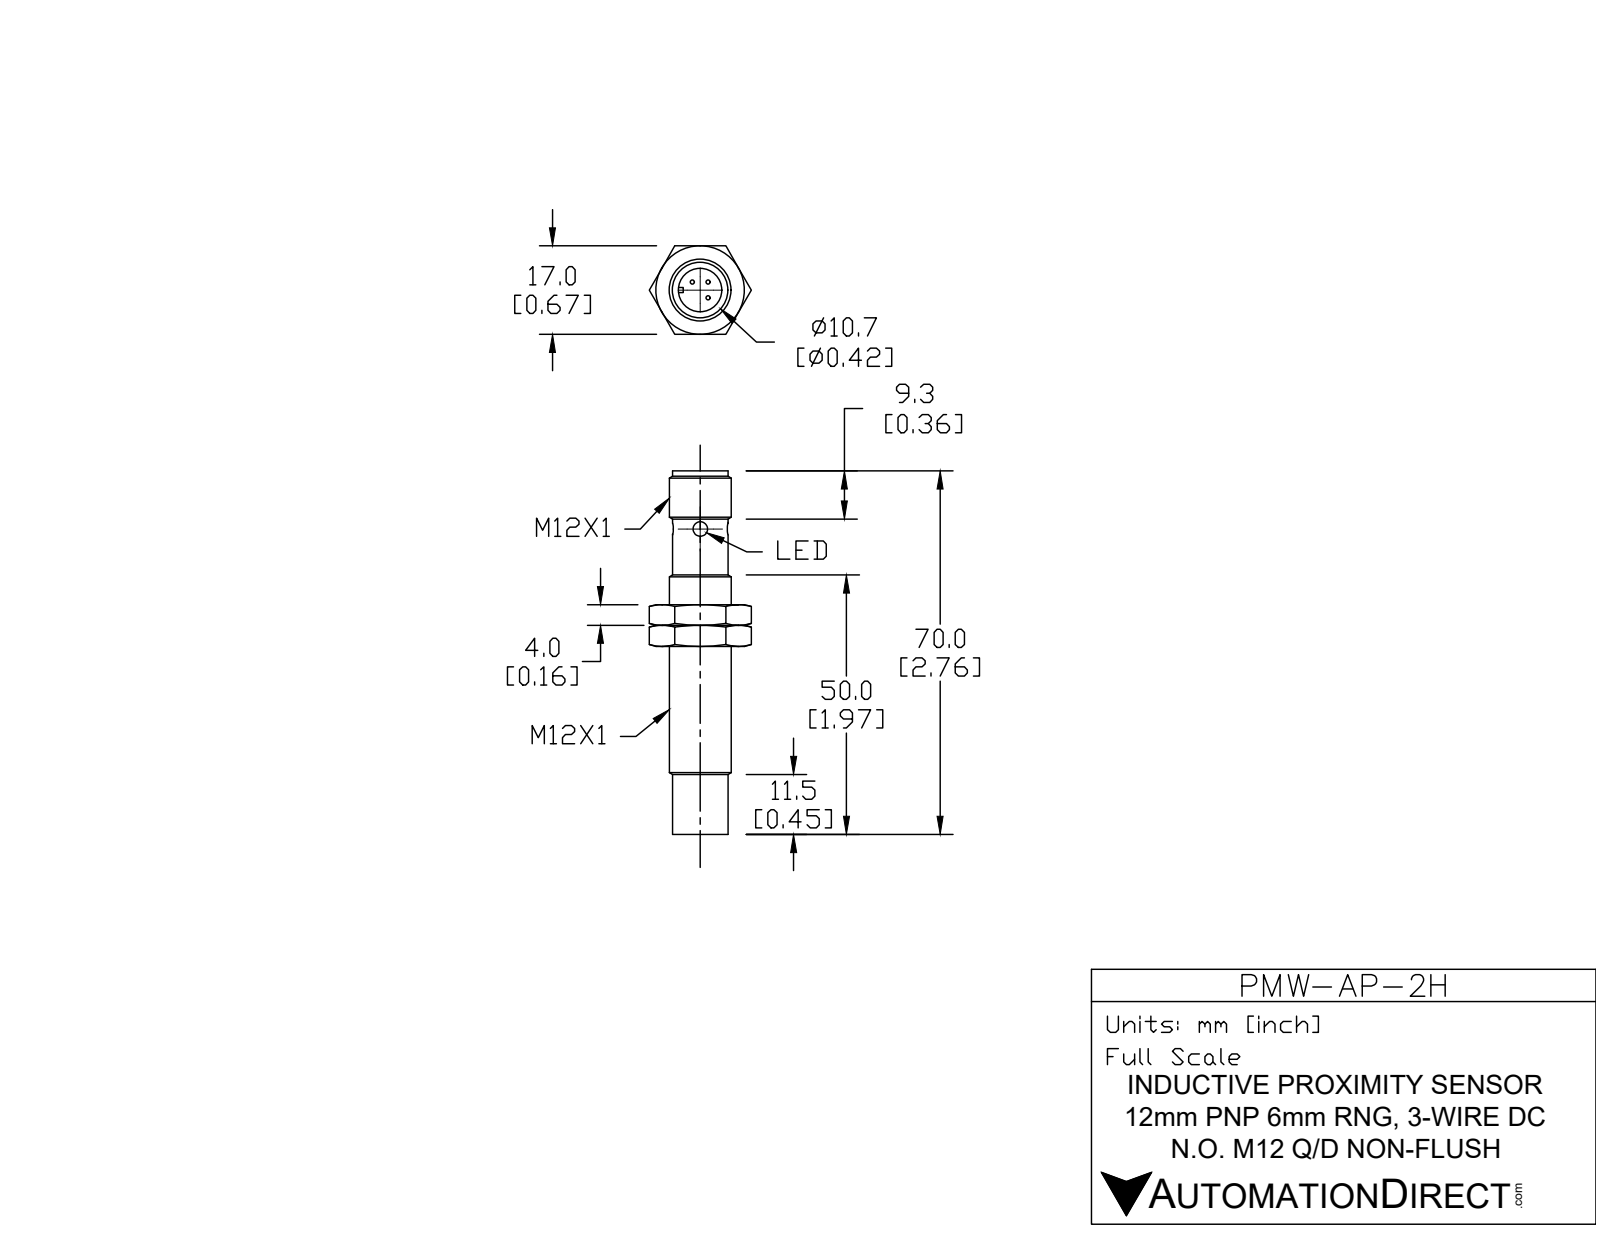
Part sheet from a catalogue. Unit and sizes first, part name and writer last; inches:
Units: inches
Overall size (bounding box): 2.764 × 0.773 × 0.669
Round holes (diameter × count): ⌀0.098 ×2, ⌀0.331 ×1, ⌀0.43 ×1
Round bosses / shafts (diameter × count): ⌀0.472 ×1, ⌀0.429 ×1
Partial cylindrical surfaces — rounded edges, fillets, slot ends (radius × count): R0.024 ×1, R0.197 ×1
Main face-to-face distances: 0.157, 0.669, 0.315, 1.11, 0.953, 0.795, 1.303, 1.461, 1.618, 2.413
Volume: 0.5 in³ · Surface area: 6.714 in²
Bodies: 3 solids, 94 faces (22 planar, 30 cylindrical, 42 other)
Part name (STEP PRODUCT): PMW-AP-2H
STEP written by: SolidWorks 2017 (AUTOMOTIVE_DESIGN)
